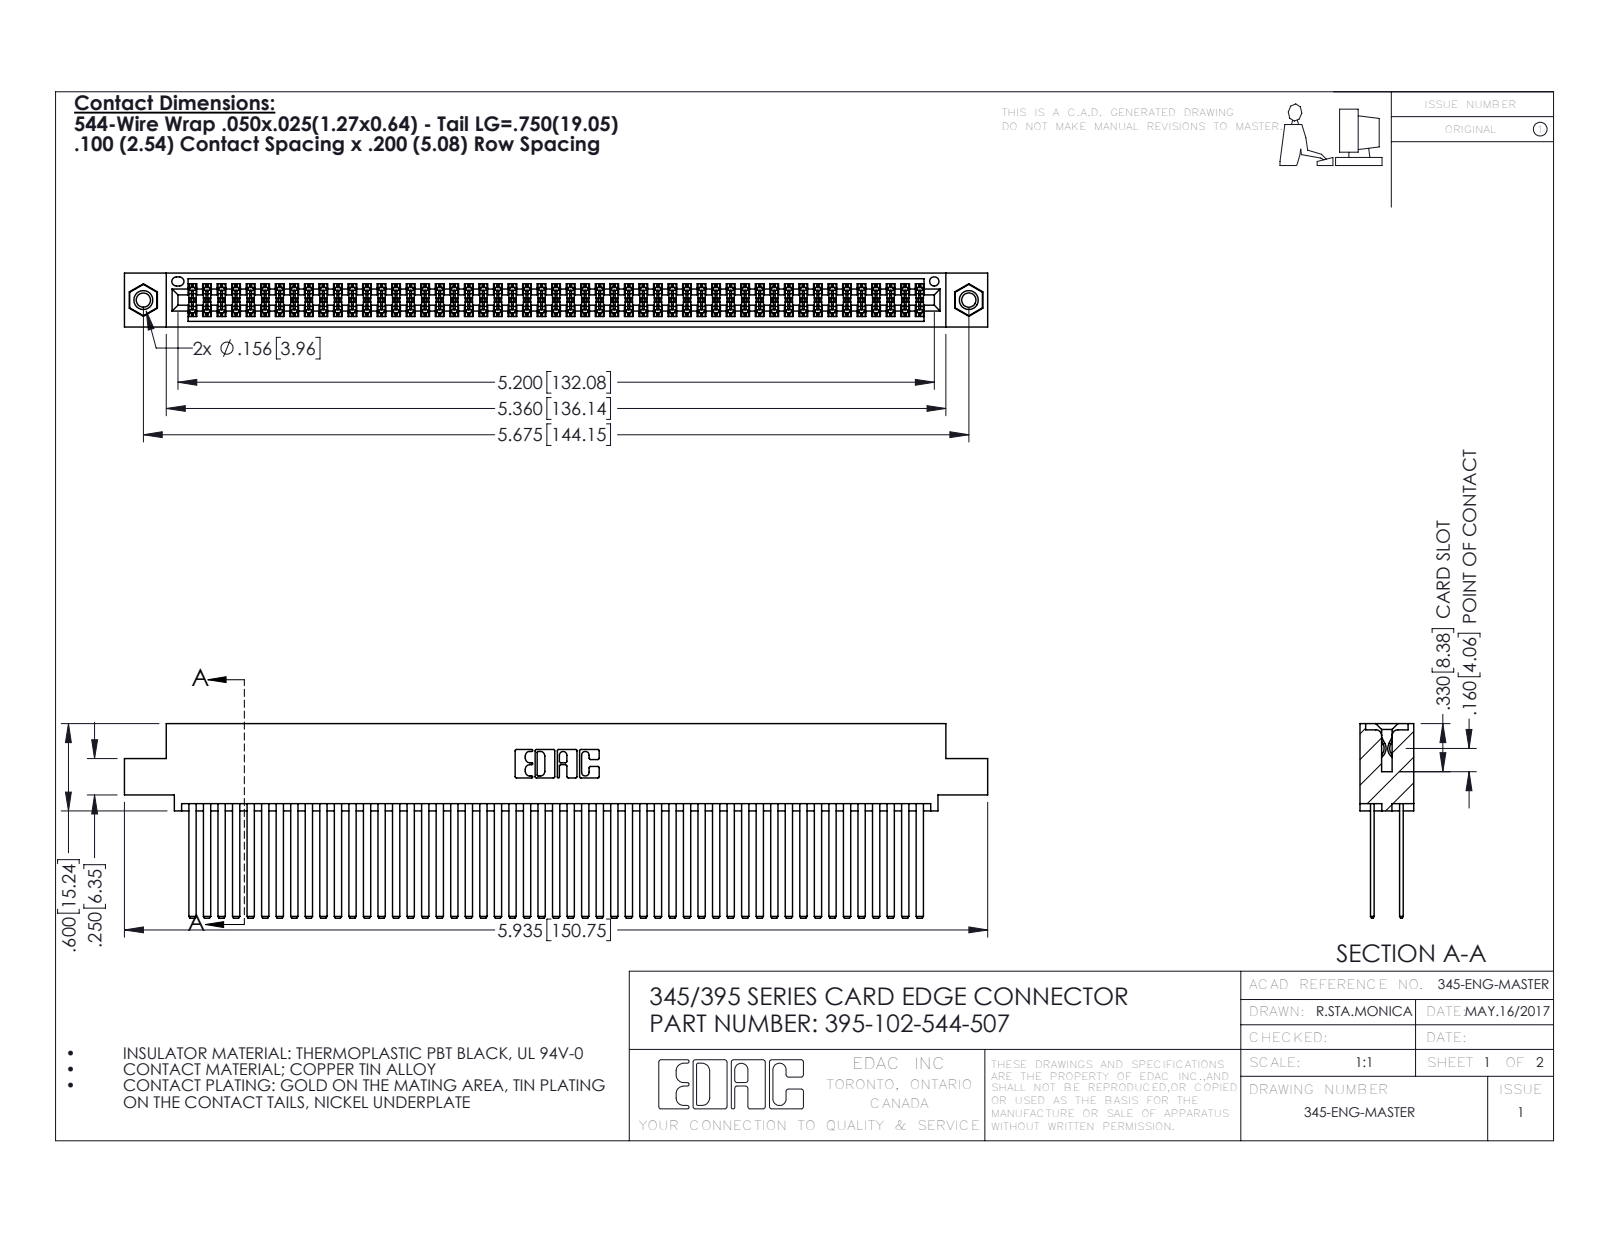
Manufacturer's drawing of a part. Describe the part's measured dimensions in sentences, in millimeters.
The part is named "345-292-001_345-293-144; 395-102-544-507; 345 Part_0.110 Offset - 0.156 Dia-TI; 345-250-001_345-250-005-103". Its 3-D file was written by "SolidWorks 2016 (CONFIG_CONTROL_DESIGN)". It is 105 solids with 4678 faces: 3074 planar, 1588 cylindrical and 16 other. Overall it measures 150.7 by 34 by 9.4 millimeters. Its volume is 16 100 cubic millimeters and its surface area 28 240 square millimeters. Round holes: 2 of diameter 2.5, 2 of diameter 3.2, 2 of diameter 4, 1 of diameter 1.6. Round bosses or shafts: 2 of diameter 3.9. Partial cylindrical surfaces (rounded edges, fillets, slot ends): 153 of radius 0.2, 22 of radius 0.3, 6 of radius 0.2, 6 of radius 0.8, 3 of radius 0.7, 2 of radius 0.4, 2 of radius 0.5, 2 of radius 0.6. The main face-to-face distances are 5.1, 0.6, 1.8, 2.5, 6.9, 7.6, 5.7, 4.4, 9.4, 1.3. The hole center spacings are 6.9, 138.2, 144.1.
